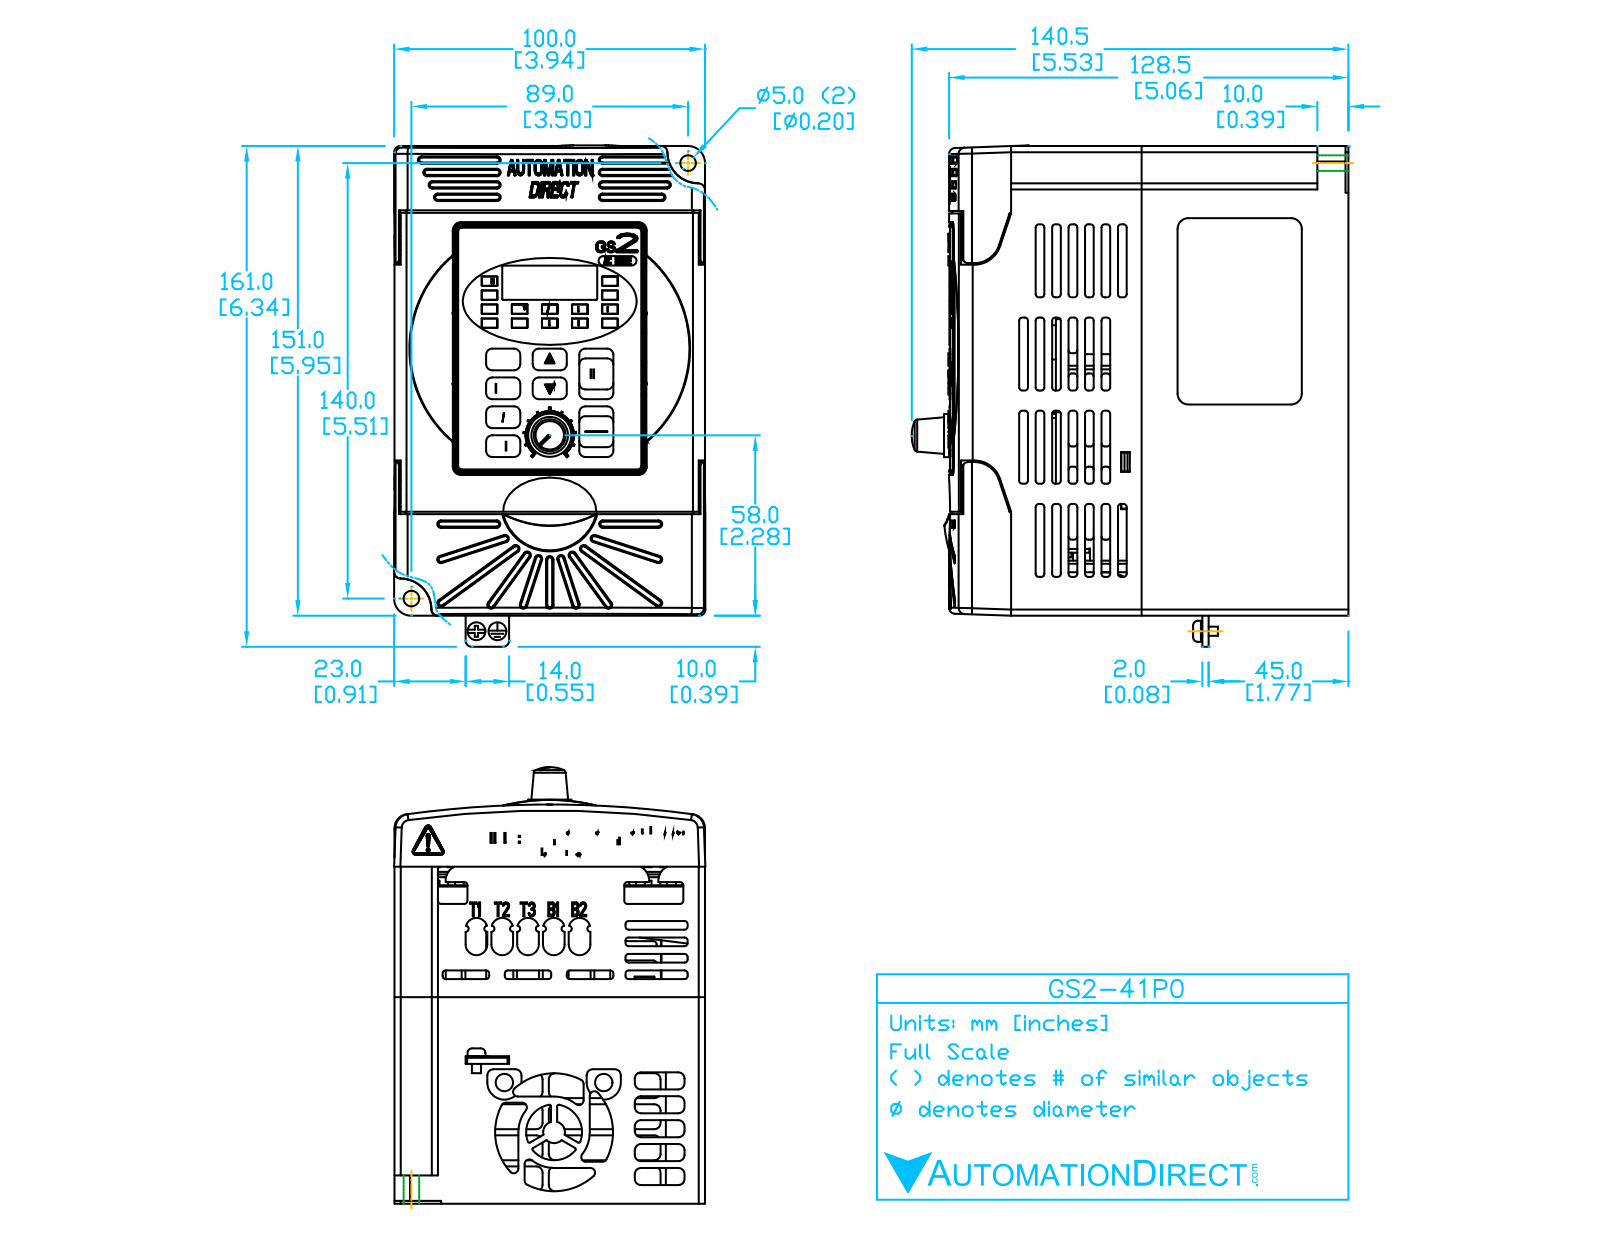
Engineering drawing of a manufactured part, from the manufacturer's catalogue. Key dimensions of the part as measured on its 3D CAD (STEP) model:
Part name (STEP PRODUCT): GS2-41P0
STEP written by: SolidWorks 2013 (AUTOMOTIVE_DESIGN)
Units: inches
Bodies: 1 solid, 738 faces (317 planar, 228 cylindrical, 193 other)
Overall size (bounding box): 6.345 × 5.495 × 3.94
Volume: 112.9 in³ · Surface area: 196.7 in²
Round holes (diameter × count): ⌀0.2 ×2, ⌀0.7 ×1, ⌀1.46 ×1
Round bosses / shafts (diameter × count): ⌀0.545 ×1, ⌀0.22 ×1, ⌀0.15 ×1
Partial cylindrical surfaces — rounded edges, fillets, slot ends (radius × count): R0.04 ×40, R0.06 ×24, R0.125 ×10, R0.02 ×8, R0.03 ×8, R0.045 ×6, R0.2 ×6, R0.1 ×4
Main face-to-face distances: 3.94, 5.95, 4.256, 4.266, 0.015, 5.935, 0.03, 0.761, 3.179, 0.03
Hole centre spacings: 6.528
